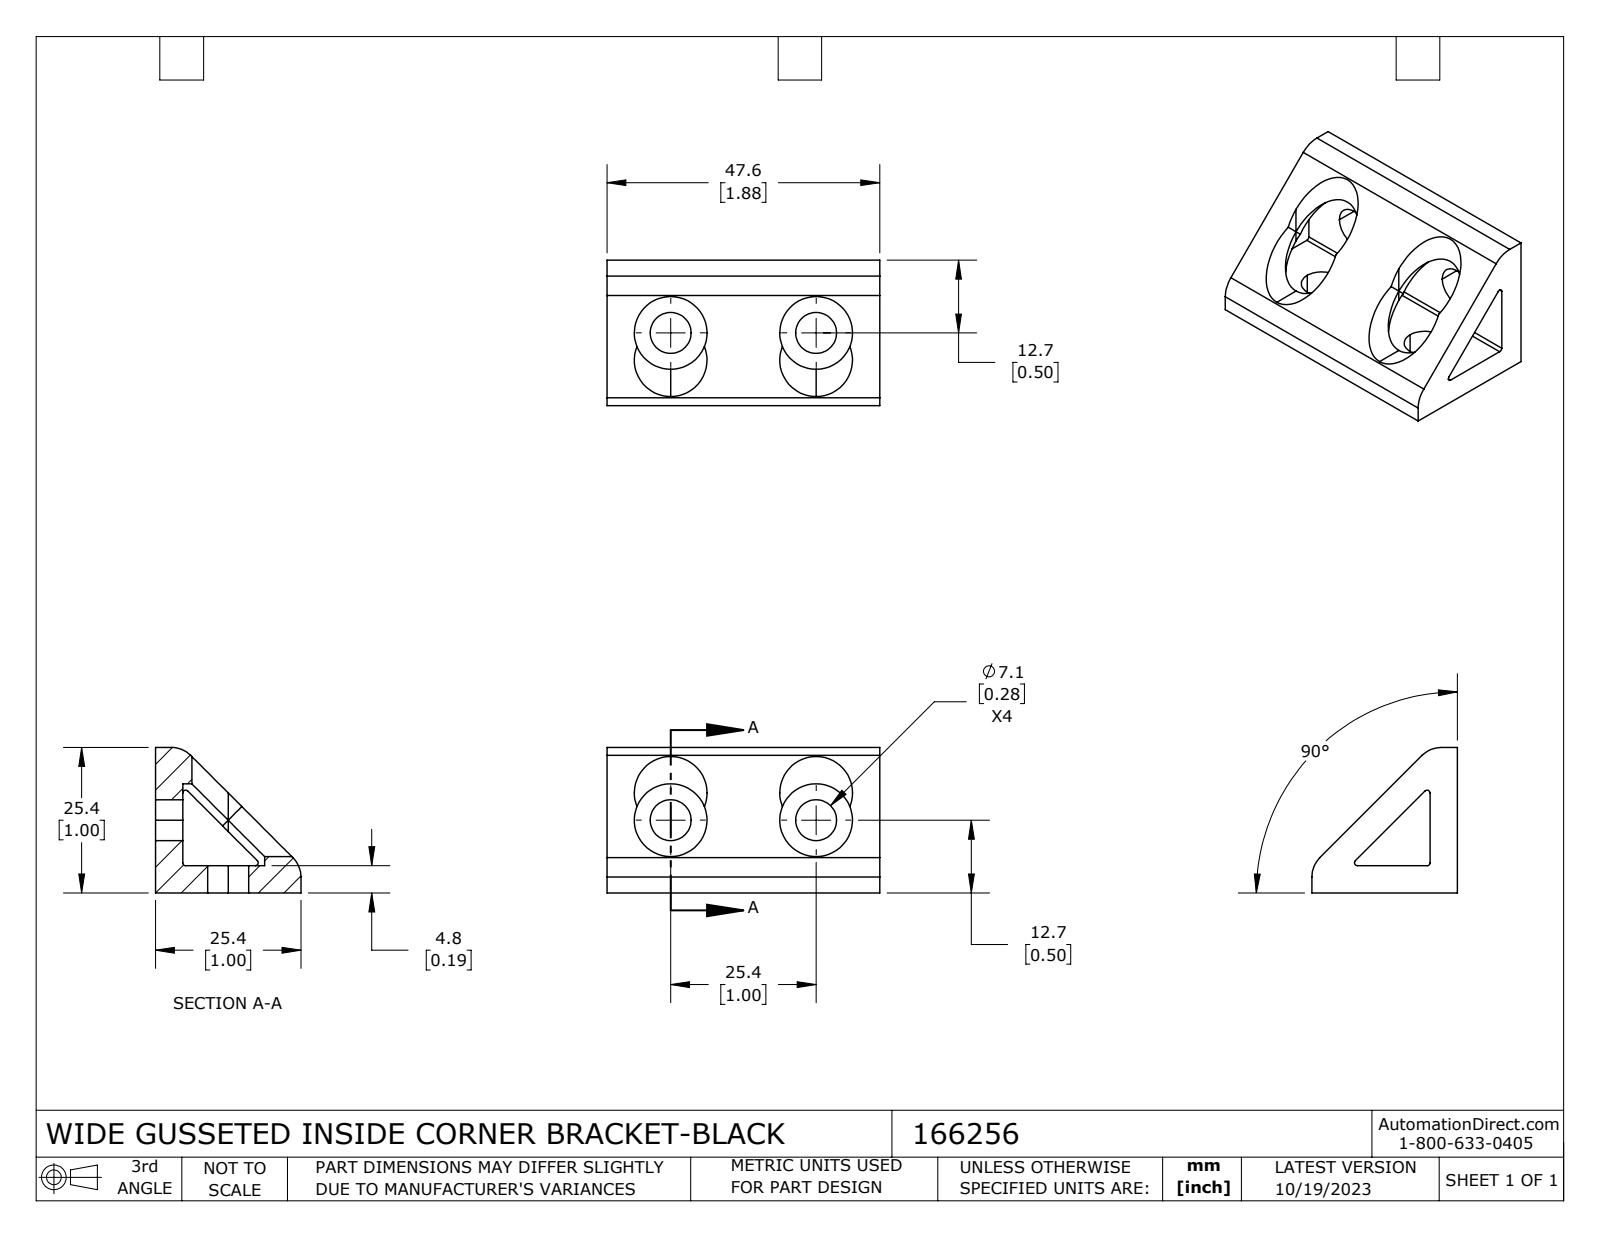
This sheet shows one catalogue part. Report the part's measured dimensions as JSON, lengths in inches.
{"part_name": "166256", "step_written_by": "SolidWorks 2023 (CONFIG_CONTROL_DESIGN)", "units": "inches", "bodies": {"solids": 1, "faces": 47, "planar": 12, "cylindrical": 35, "other": 0}, "overall_size": [1.875, 1, 1], "volume_in3": 0.803, "surface_area_in2": 10.58, "round_holes": [[0.281, 4], [0.5, 4]], "partial_cylinders_radius": [[0.02, 3], [0.187, 1], [0.188, 1]], "face_to_face_distances": [0.187, 1.875, 1, 0.813], "hole_center_spacings": [1]}
